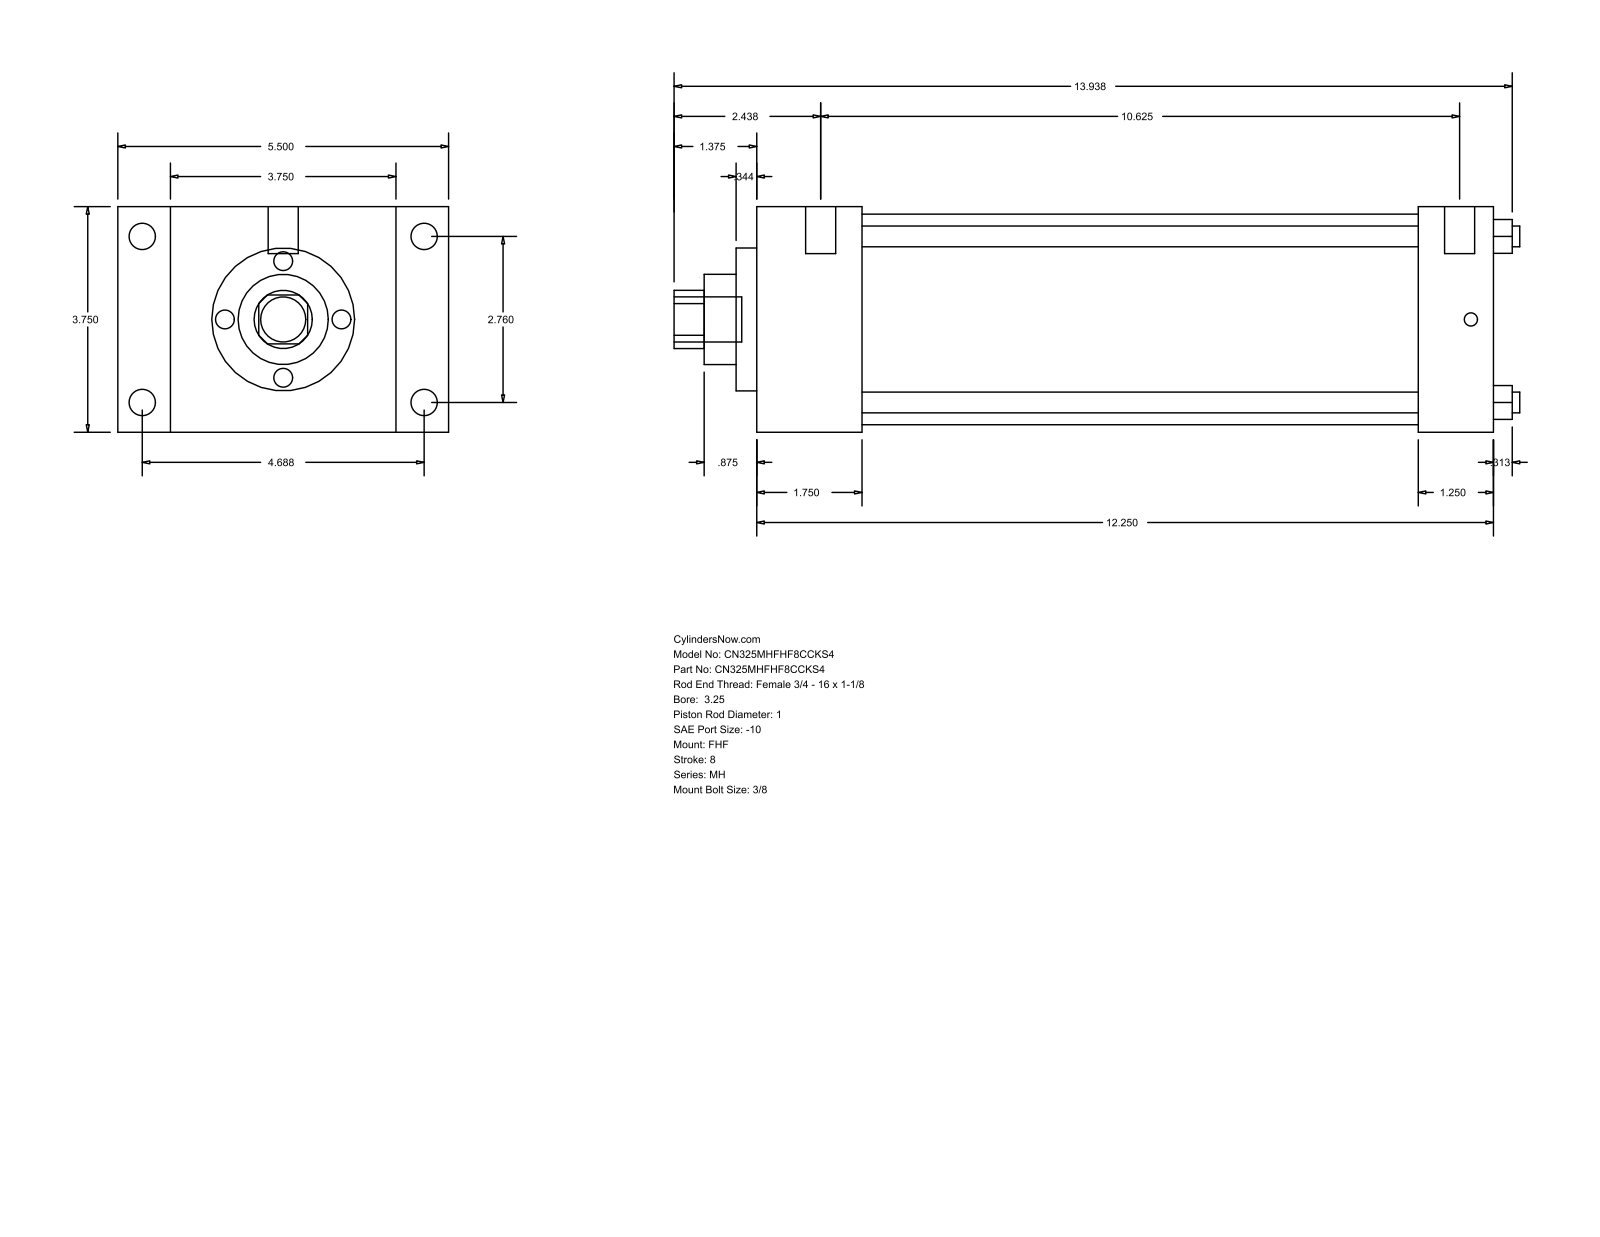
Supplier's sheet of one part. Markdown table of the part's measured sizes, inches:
| quantity | value |
| --- | --- |
| part name | MH_FHF__0325_1 |
| STEP written by | GSSL Pune (CONFIG_CONTROL_DESIGN) |
| units | inches |
| bodies | 0 solids, 90 faces (61 planar, 29 cylindrical, 0 other) |
| overall size | 14.063 × 5.5 × 3.75 |
| round holes (diameter × count) | 0.345 × 4, 1 × 1, 1.5 × 1, 2.375 × 1, 3.5 × 1 |
| round bosses / shafts (diameter × count) | 0.438 × 4, 0.219 × 4, 0.5 × 2, 0.75 × 1 |
| partial cylindrical surfaces (radius × count) | 0.484 × 1 |
| main face-to-face distances | 3.75, 12.25, 1.75, 10.5, 0.875, 4.625, 5.5, 11, 9.25, 1.25 |
| hole center spacings | 1.952, 2.76, 3.903 |
